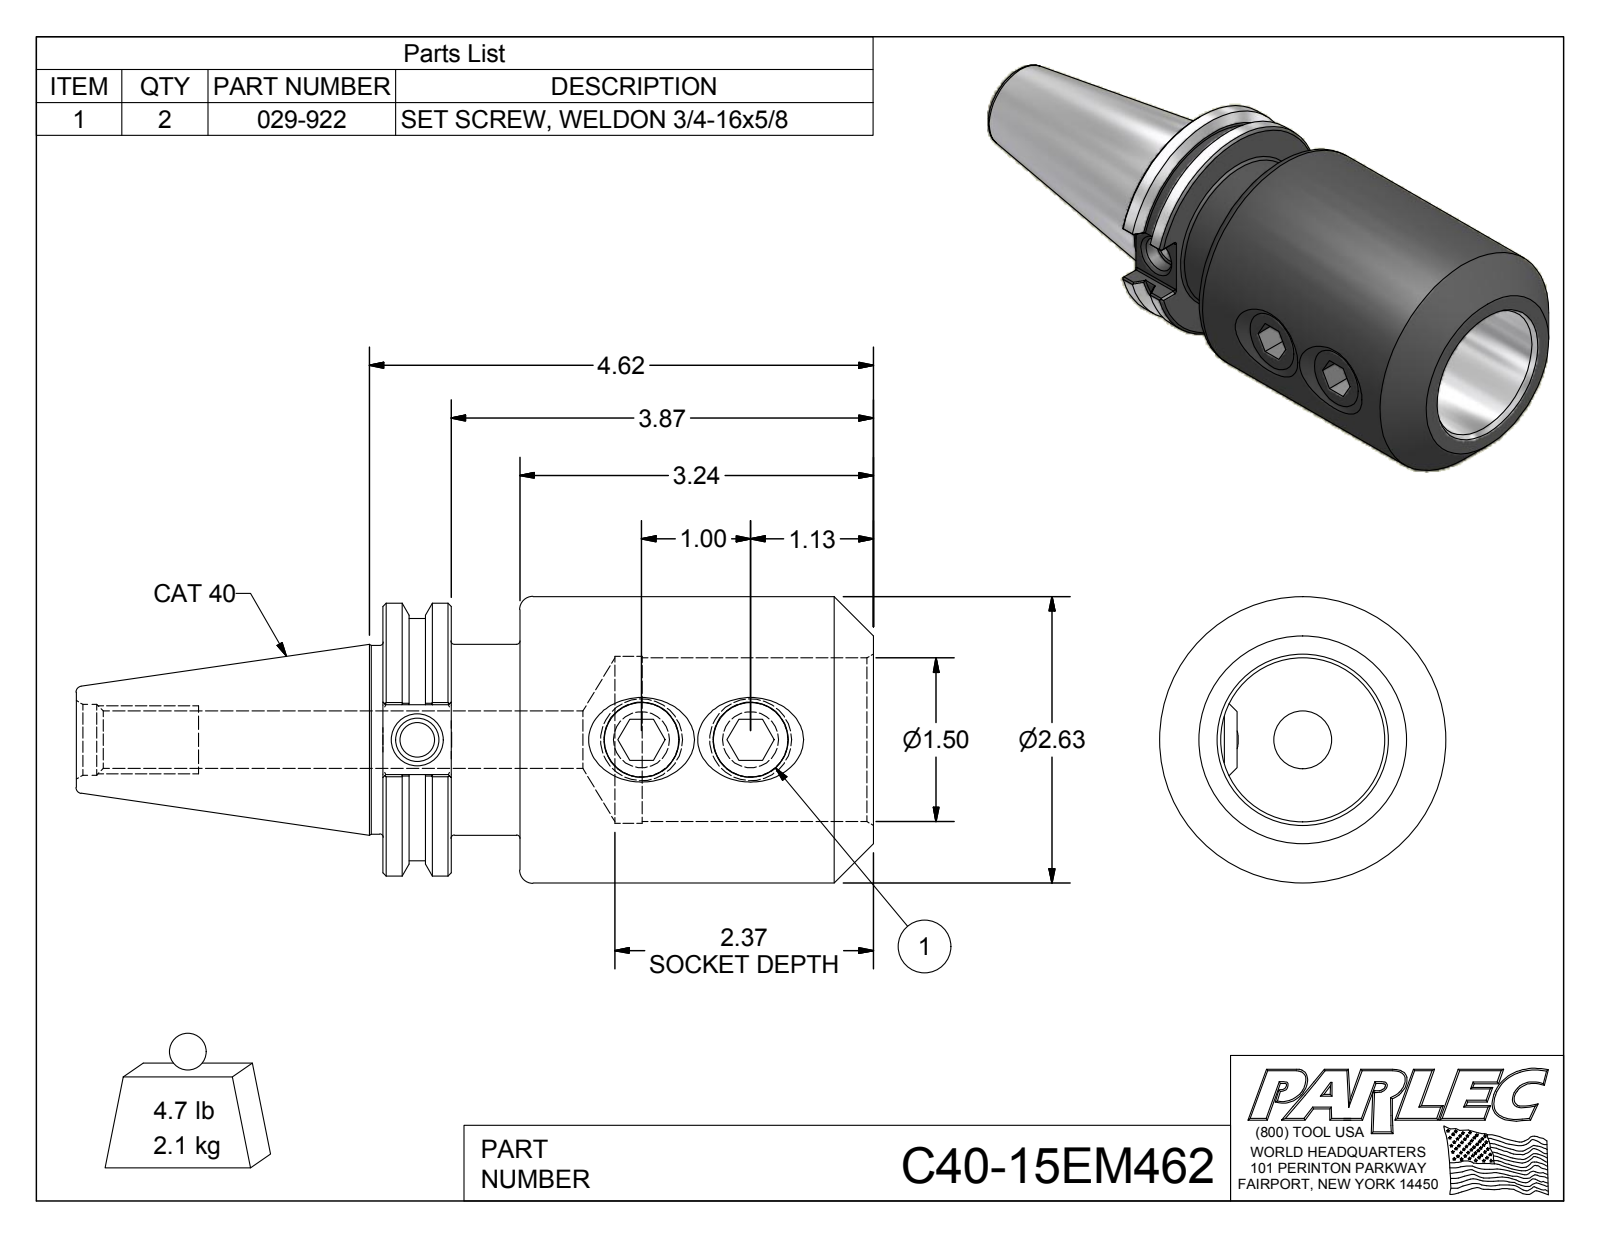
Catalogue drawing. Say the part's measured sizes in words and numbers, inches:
The part is named "C40-15EM462; C40-15EM462-1; 029-922". Its 3-D file was written by "Autodesk Inventor 2012 (AUTOMOTIVE_DESIGN)". It is 3 solids with 119 faces: 52 planar, 31 cylindrical and 36 other. Overall it measures 7.307 by 2.625 by 2.625 inches. Its volume is 19.93 cubic inches and its surface area 84.51 square inches. Round holes: 2 of diameter 0.682, 1 of diameter 0.315, 1 of diameter 0.399, 1 of diameter 0.527, 1 of diameter 0.648, 1 of diameter 1.5, 1 of diameter 1.53. Round bosses or shafts: 2 of diameter 0.75, 1 of diameter 2.625, 1 of diameter 2.5, 1 of diameter 2.219, 1 of diameter 1.75, 1 of diameter 1.73. Partial cylindrical surfaces (rounded edges, fillets, slot ends): 12 of radius 0.02. The main face-to-face distances are 1.255, 0.625, 0.63, 4.495, 3.87, 3.24, 0.866, 0.625, 0.375, 1.489. The hole center spacings are 1, 2.055, 3.055.
